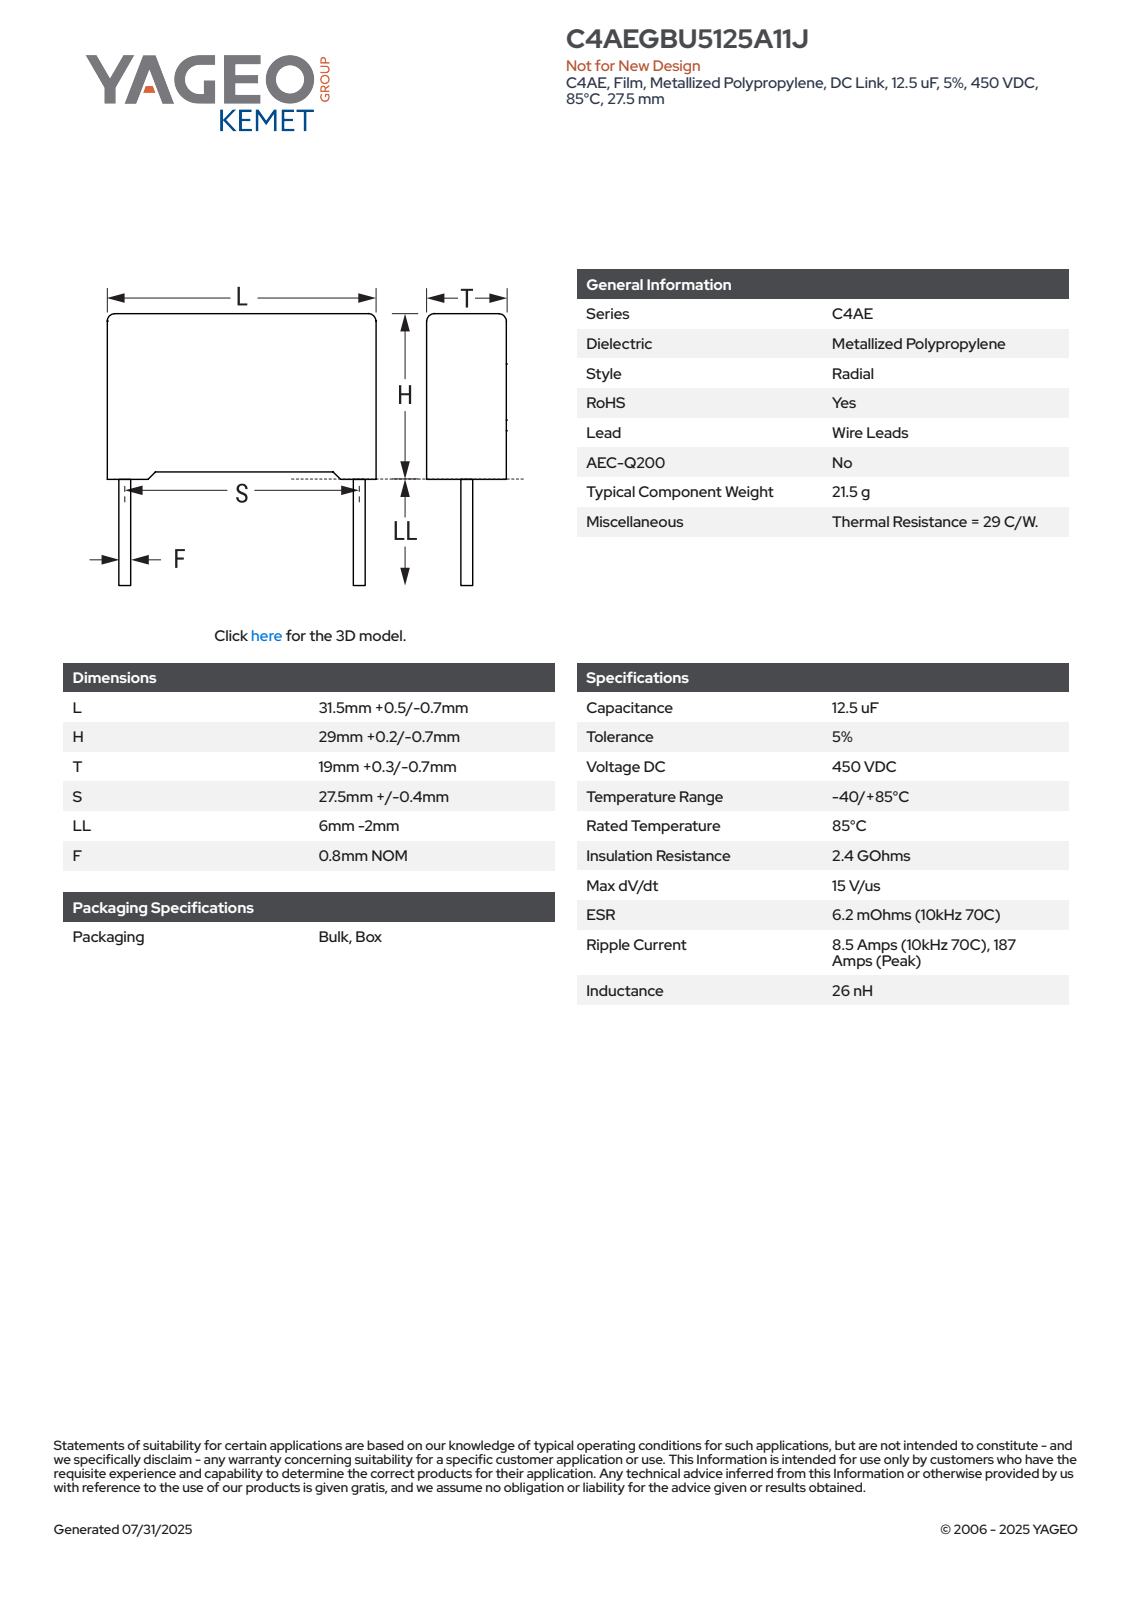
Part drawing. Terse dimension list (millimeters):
name: CFR_RB2CFP_31.5X29X19_L32H29.2T19.3S27.5LL4F0.8
written by: SolidWorks 2014 (AUTOMOTIVE_DESIGN)
unit: mm
bodies: 4 solids, 85 faces (77 planar, 8 cylindrical, 0 other)
size: 33.2 × 32 × 19.3
volume: 17 497 mm³; area: 4 303 mm²
bosses: 2× ⌀0.8
rounds: 4× R0.5
face distances: 19.3, 32, 28.19, 28.45, 0.75, 1.01, 29.2, 1.07, 30.93, 19.31
